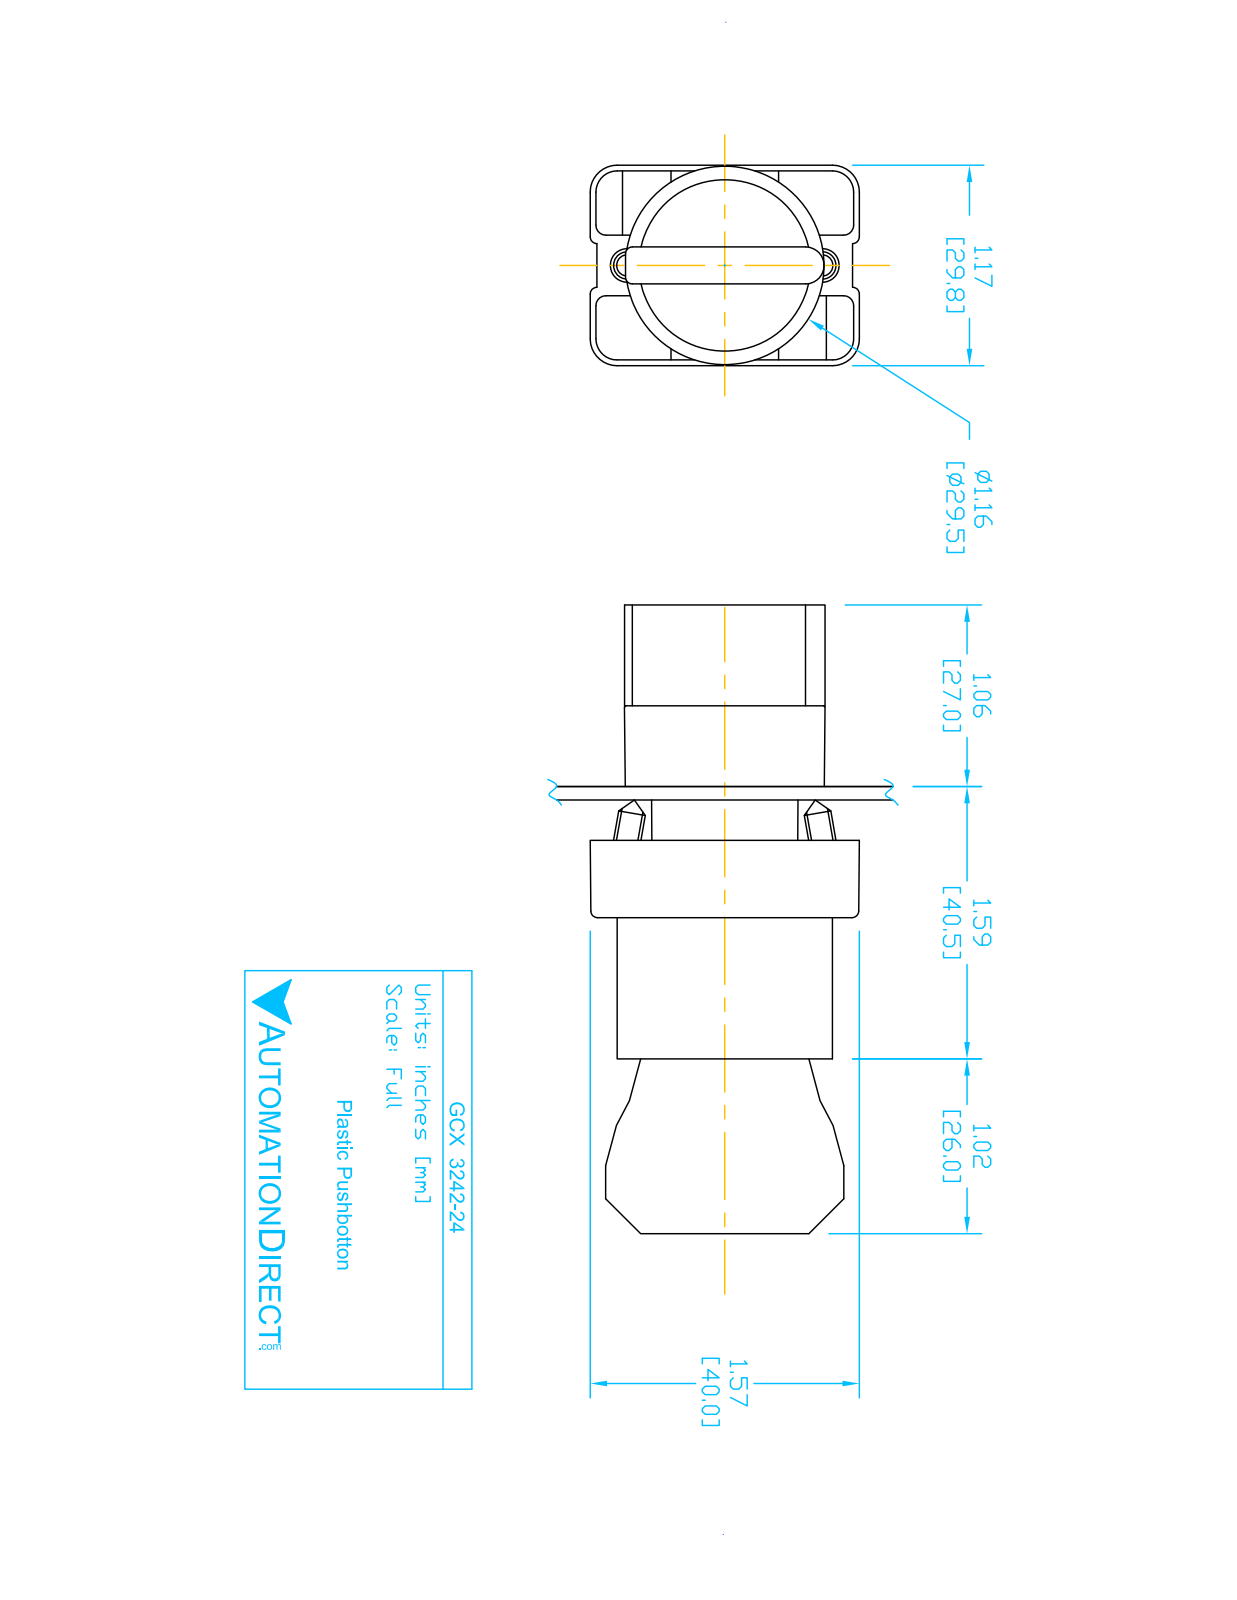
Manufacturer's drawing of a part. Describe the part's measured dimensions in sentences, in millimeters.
The part is named "GCX3242-24; ECX1050; GCX3242 OPERATOR; ecx1040 (+1 more)". Its 3-D file was written by "SolidWorks 2016 (AUTOMOTIVE_DESIGN)". It is 8 solids with 445 faces: 263 planar, 151 cylindrical and 31 other. Overall it measures 92.8 by 40.2 by 29.9 millimeters. Its volume is 45 870 cubic millimeters and its surface area 25 160 square millimeters. Round holes: 2 of diameter 2, 2 of diameter 3.1, 2 of diameter 3.3, 1 of diameter 2.2, 1 of diameter 5, 1 of diameter 11.9, 1 of diameter 22.3, 1 of diameter 22.6, 1 of diameter 26. Round bosses or shafts: 4 of diameter 4, 1 of diameter 29.8, 1 of diameter 25.5, 1 of diameter 24, 1 of diameter 21.7, 1 of diameter 19.8, 1 of diameter 12.8. Partial cylindrical surfaces (rounded edges, fillets, slot ends): 24 of radius 1.5, 12 of radius 1, 12 of radius 3.1, 12 of radius 4, 9 of radius 1, 2 of radius 3.3, 1 of radius 0.5, 1 of radius 1.6. The main face-to-face distances are 21, 51.3, 30.3, 14.7, 31.6, 29.7, 12, 11.9, 0.8, 0.8. The hole center spacings are 6, 13.8, 12, 12.4.
